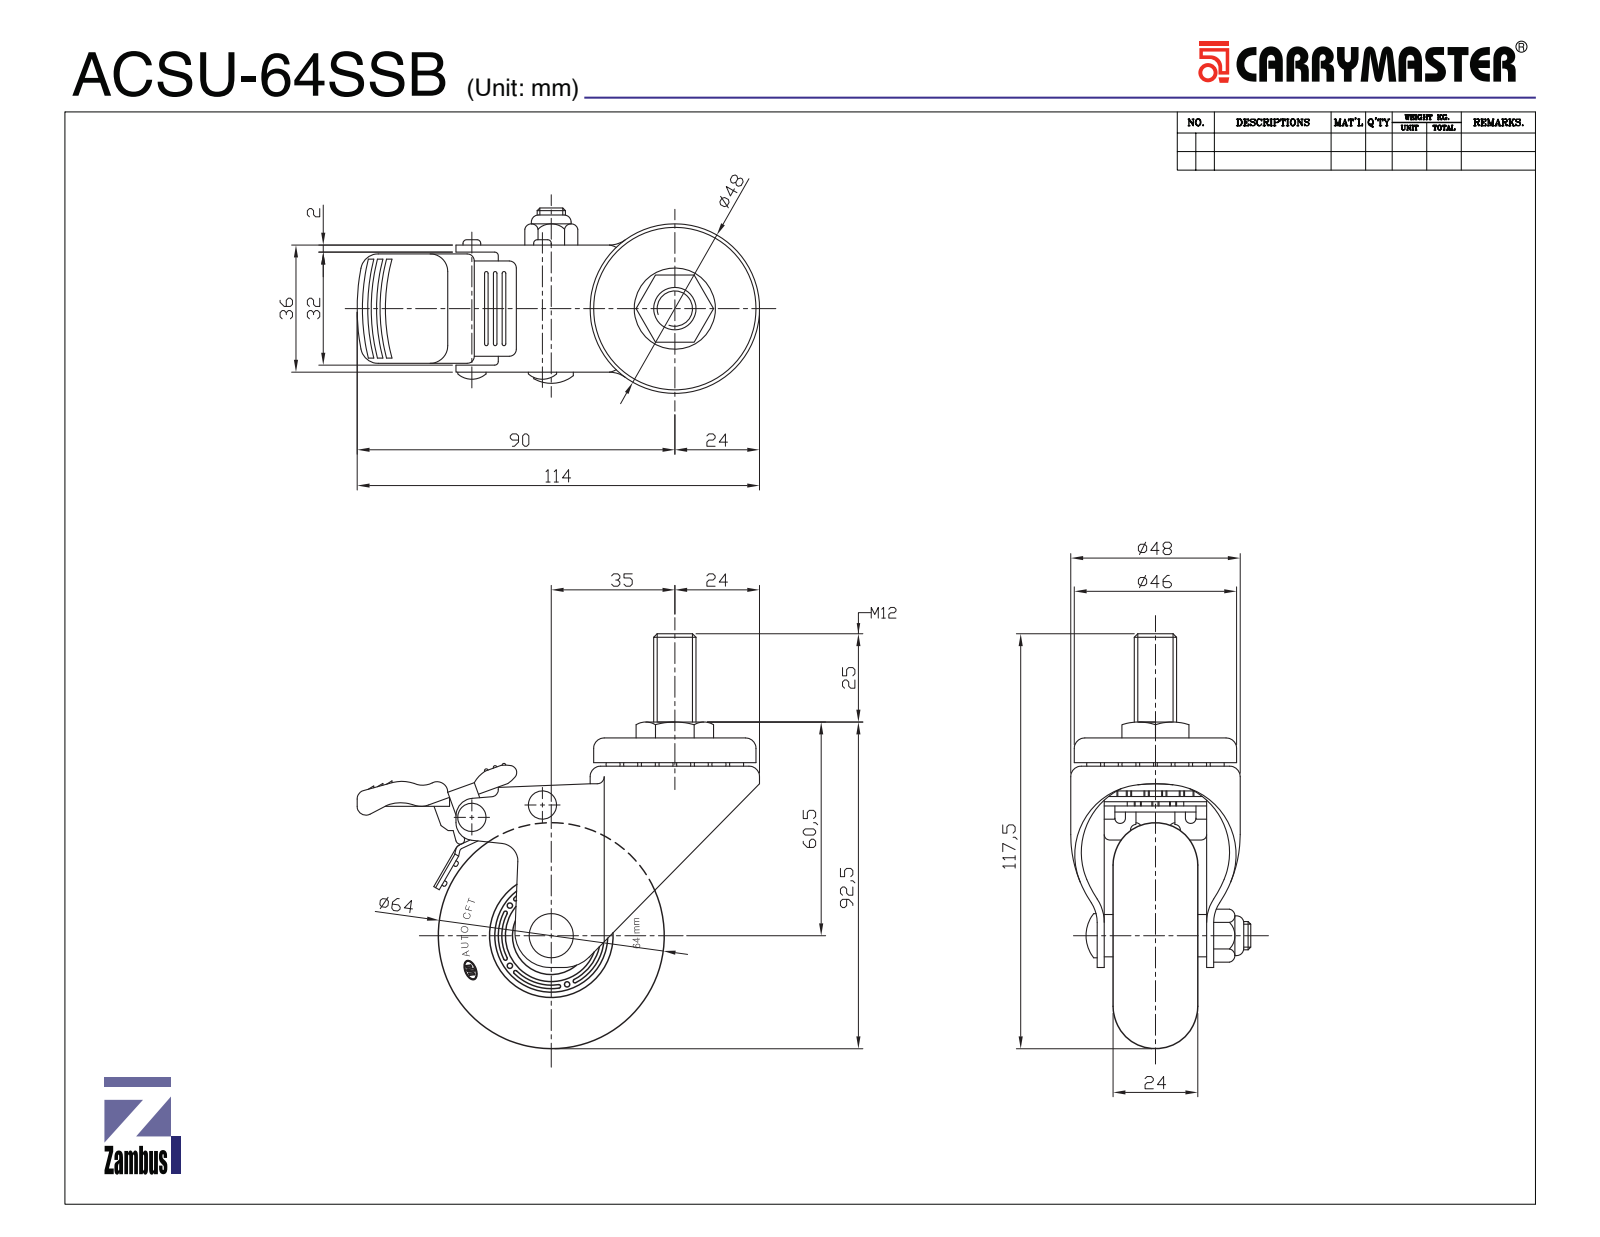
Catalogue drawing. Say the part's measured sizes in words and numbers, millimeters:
The part is named "ACSU-64SSB". Its 3-D file was written by "SolidWorks 2015 (CONFIG_CONTROL_DESIGN)". It is 22 solids with 1113 faces: 408 planar, 444 cylindrical and 261 other. Overall it measures 118.91 by 113.76 by 49.2 millimeters. Its volume is 110 990 cubic millimeters and its surface area 75 905 square millimeters. Round holes: 2 of diameter 3.5, 2 of diameter 4, 1 of diameter 6.8, 1 of diameter 8, 1 of diameter 8.1, 1 of diameter 11, 1 of diameter 12.67, 1 of diameter 17.33, 1 of diameter 18.5, 1 of diameter 22, 1 of diameter 27, 1 of diameter 35. Round bosses or shafts: 2 of diameter 4.9, 1 of diameter 47.5, 1 of diameter 42.4, 1 of diameter 30.3, 1 of diameter 18, 1 of diameter 16, 1 of diameter 12.5, 1 of diameter 12. Partial cylindrical surfaces (rounded edges, fillets, slot ends): 63 of radius 1, 44 of radius 0.75, 26 of radius 1.25, 21 of radius 0.5, 13 of radius 1.5, 12 of radius 2, 8 of radius 8, 7 of radius 2.5. The main face-to-face distances are 2, 35.5, 1.5, 3.5, 37.5, 33.5, 1.41, 6.75, 30.75, 4.75. The hole center spacings are 20.93, 36.67, 40.24.
